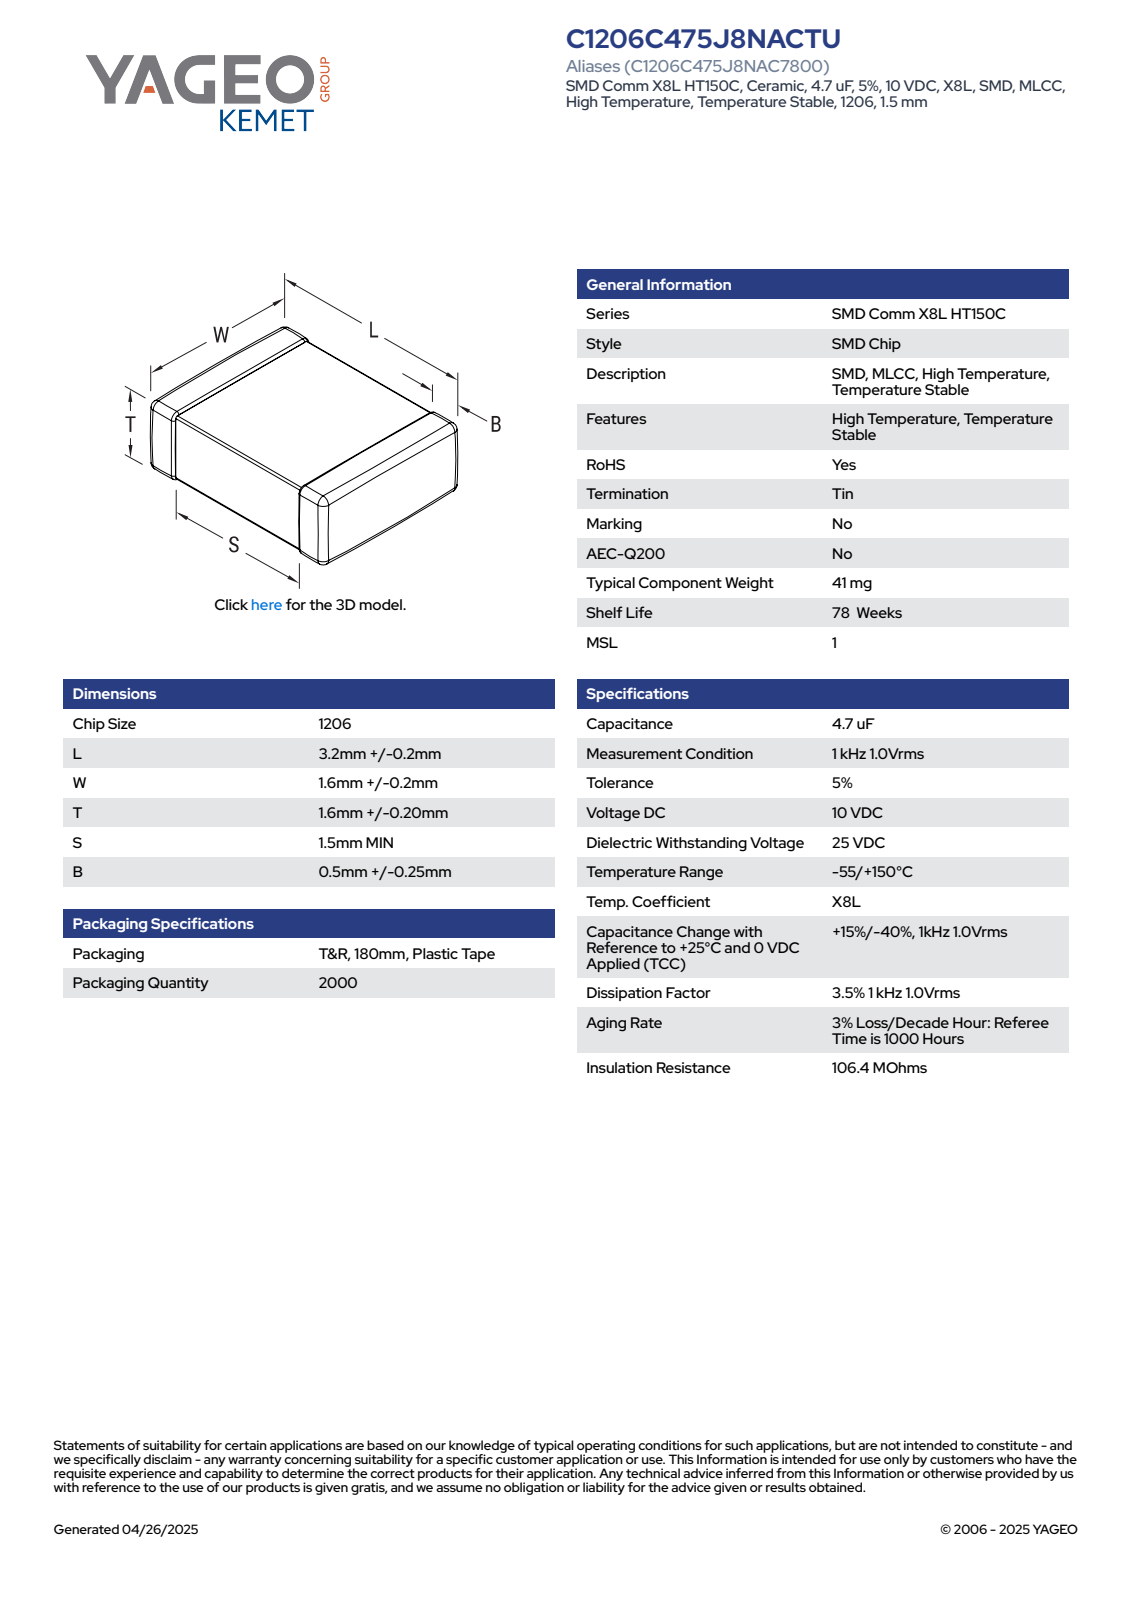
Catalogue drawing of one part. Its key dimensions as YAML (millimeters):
part_name: "CCS_CCSTD_1206_L3.4W1.8S1.6T1.8B0.5"
step_written_by: "SolidWorks 2021 (AUTOMOTIVE_DESIGN)"
units: millimeters
bodies: {solids: 4, faces: 125, planar: 71, cylindrical: 38, other: 16}
overall_size: [3.4, 1.8, 1.8]
volume: 11
surface_area: 31
face_to_face_distances: [1.76, 1.72, 1.8, 3.4, 1.73, 1.77, 1.57, 1.83, 1.84, 1.56]
